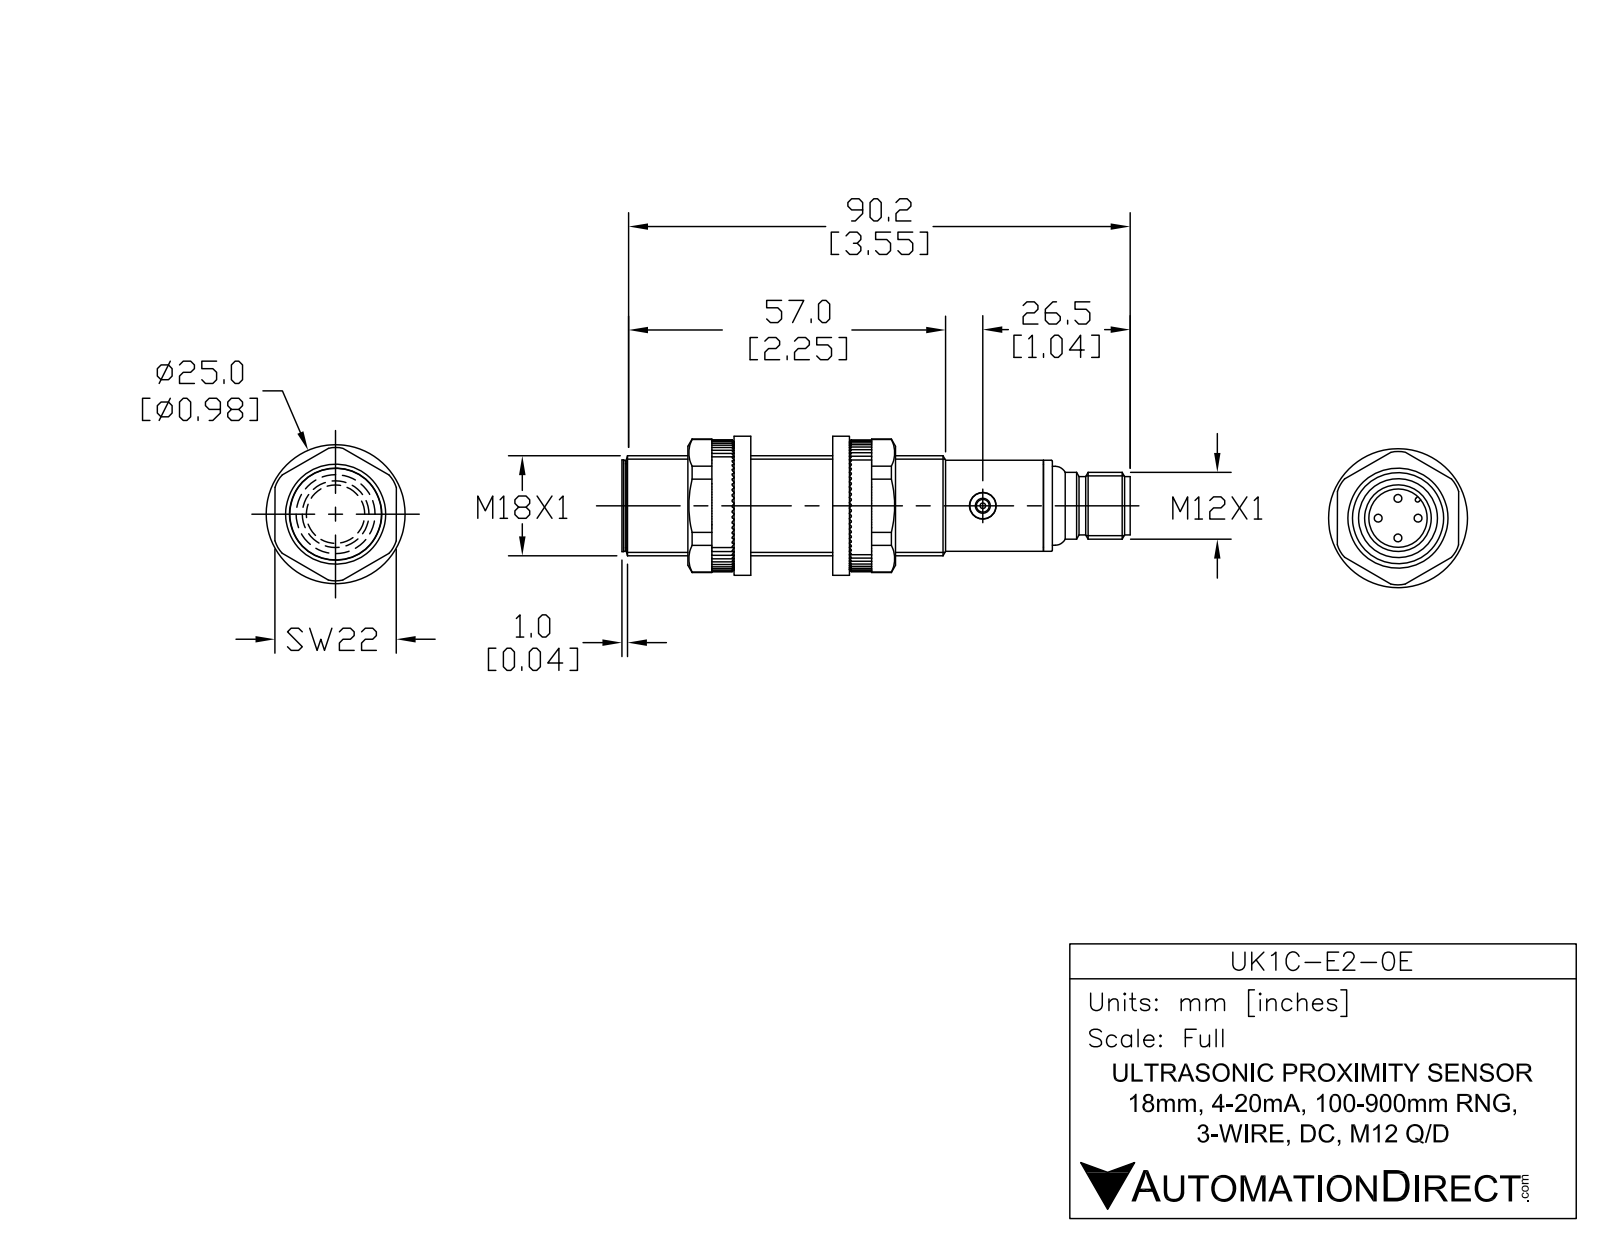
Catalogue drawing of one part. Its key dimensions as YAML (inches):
part_name: "UK1C-E2-0E"
step_written_by: "SolidWorks 2017 (AUTOMOTIVE_DESIGN)"
units: inches
bodies: {solids: 6, faces: 106, planar: 21, cylindrical: 48, other: 37}
overall_size: [3.606, 0.709, 0.709]
volume: 1.202
surface_area: 10.68
round_holes:
  - {diameter: 0.106, count: 1}
  - {diameter: 0.185, count: 1}
  - {diameter: 0.276, count: 1}
  - {diameter: 0.327, count: 1}
  - {diameter: 0.374, count: 1}
round_bosses_or_shafts:
  - {diameter: 0.039, count: 4}
  - {diameter: 0.709, count: 1}
  - {diameter: 0.654, count: 1}
  - {diameter: 0.646, count: 1}
  - {diameter: 0.622, count: 1}
  - {diameter: 0.559, count: 1}
  - {diameter: 0.472, count: 1}
  - {diameter: 0.413, count: 1}
partial_cylinders:
  - {radius: 0.024, count: 1}
face_to_face_distances: [2.957, 0.039, 2.996, 0.037, 2.994, 0.043, 0.157, 3.055, 3.053, 3.016]
